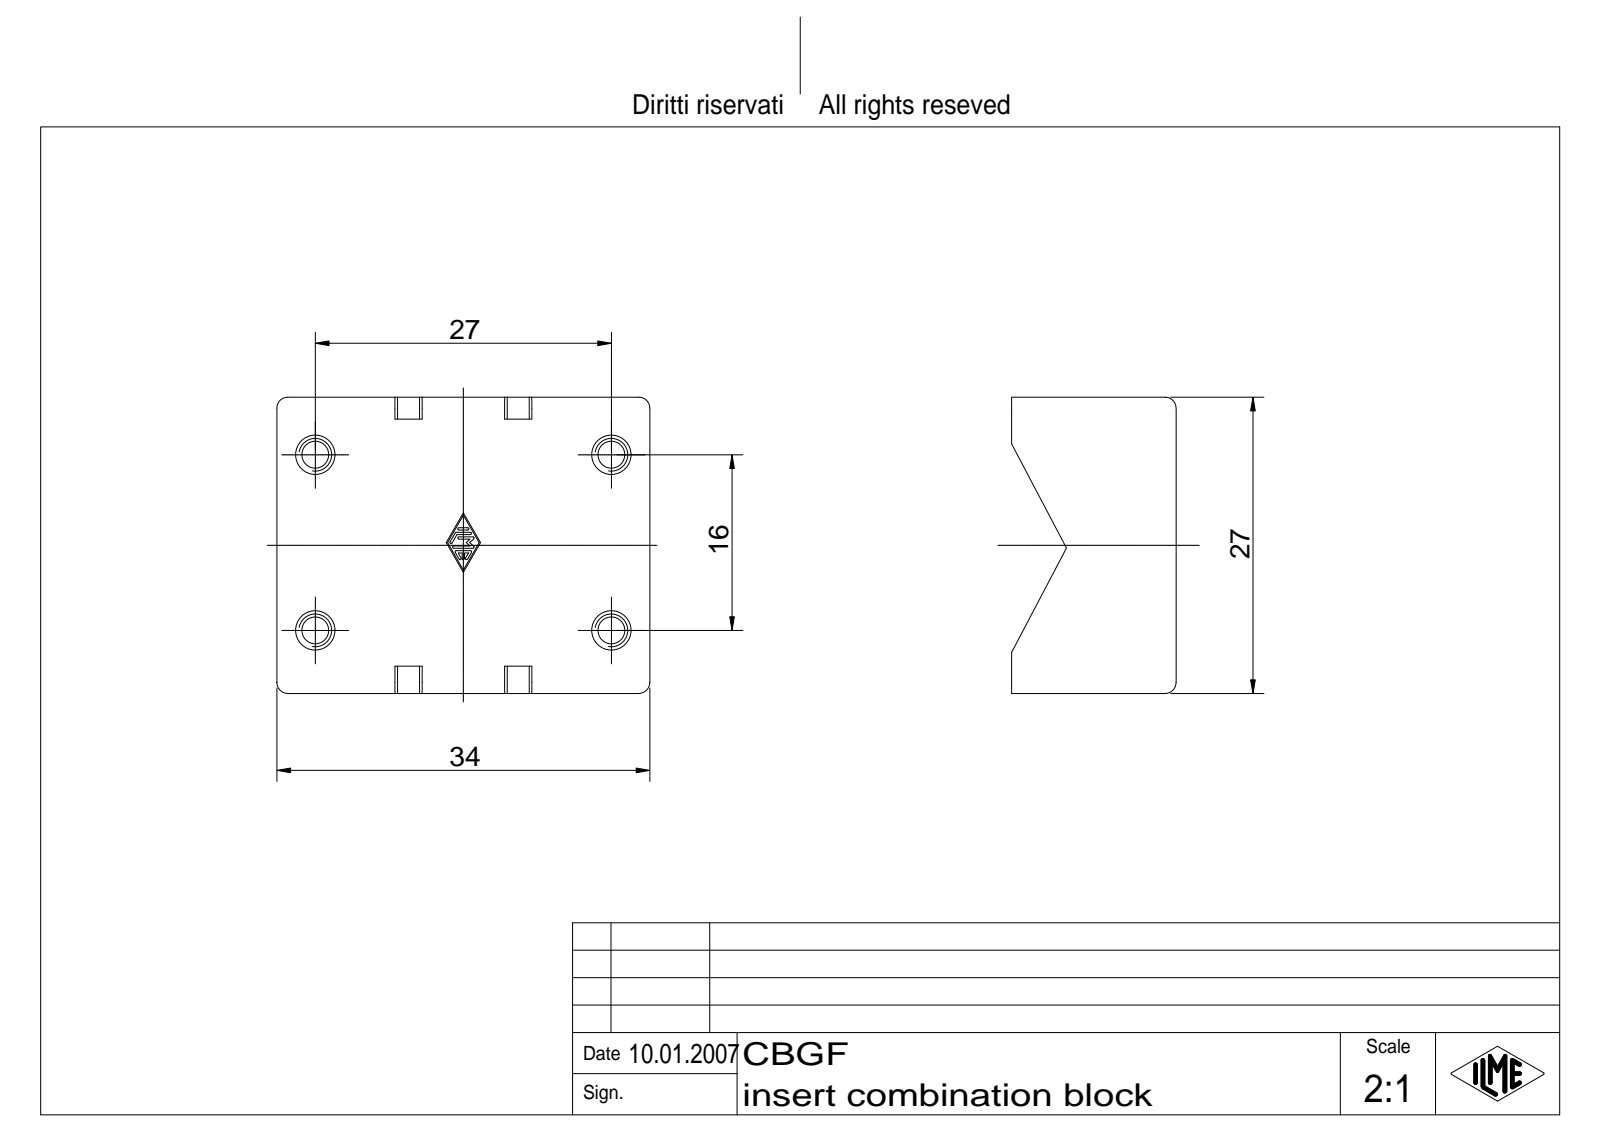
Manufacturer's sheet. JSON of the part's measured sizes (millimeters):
{"part_name": "CBGF", "step_written_by": "Autodesk Inventor 7 (AUTOMOTIVE_DESIGN)", "units": "millimeters", "bodies": {"solids": 1, "faces": 155, "planar": 73, "cylindrical": 48, "other": 34}, "overall_size": [34, 27, 15], "volume_mm3": 4951, "surface_area_mm2": 5121, "round_holes": [[4.5, 1]], "partial_cylinders_radius": [[0.1, 14], [1, 8], [3, 4]], "face_to_face_distances": [1.5, 27, 34, 2.25, 31.75, 2, 2.5, 25, 24.5, 22.5]}
